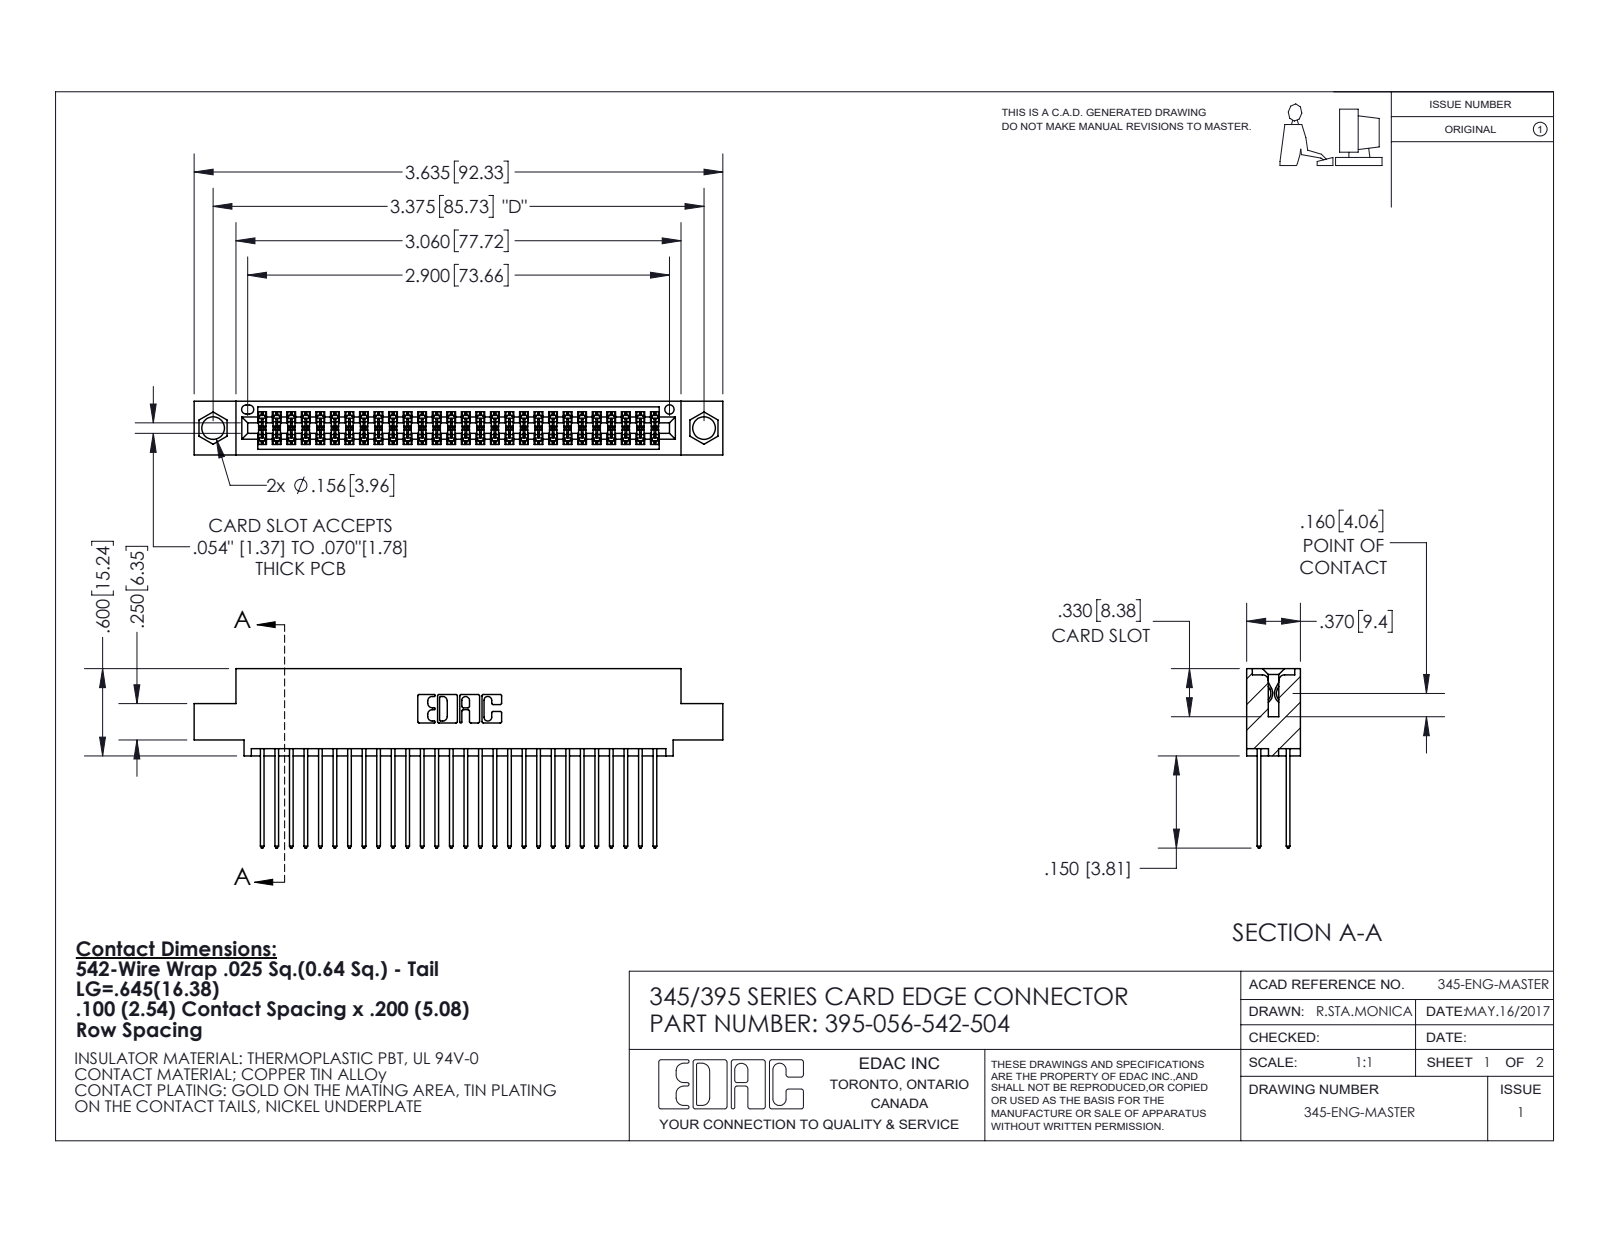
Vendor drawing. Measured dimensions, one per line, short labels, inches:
name: 345-292-001_345-293-142; 395-056-542-504; 345 Part_0.110 Offset - 0.156 Dia-TI
written by: SolidWorks 2020 (CONFIG_CONTROL_DESIGN)
unit: in
bodies: 57 solids, 2944 faces (1946 planar, 998 cylindrical, 0 other)
size: 3.635 × 1.232 × 0.37
volume: 0.544 in³; area: 21.82 in²
holes: 2× ⌀0.156, 1× ⌀0.064
rounds: 112× R0.006, 56× R0.01, 22× R0.01, 6× R0.007, 6× R0.031, 3× R0.026, 2× R0.014, 2× R0.019
face distances: 0.072, 0.298, 0.2, 0.098, 0.272, 0.025, 0.37, 0.225, 0.175, 0.149
hole spacings: 0.27, 3.14, 3.375
